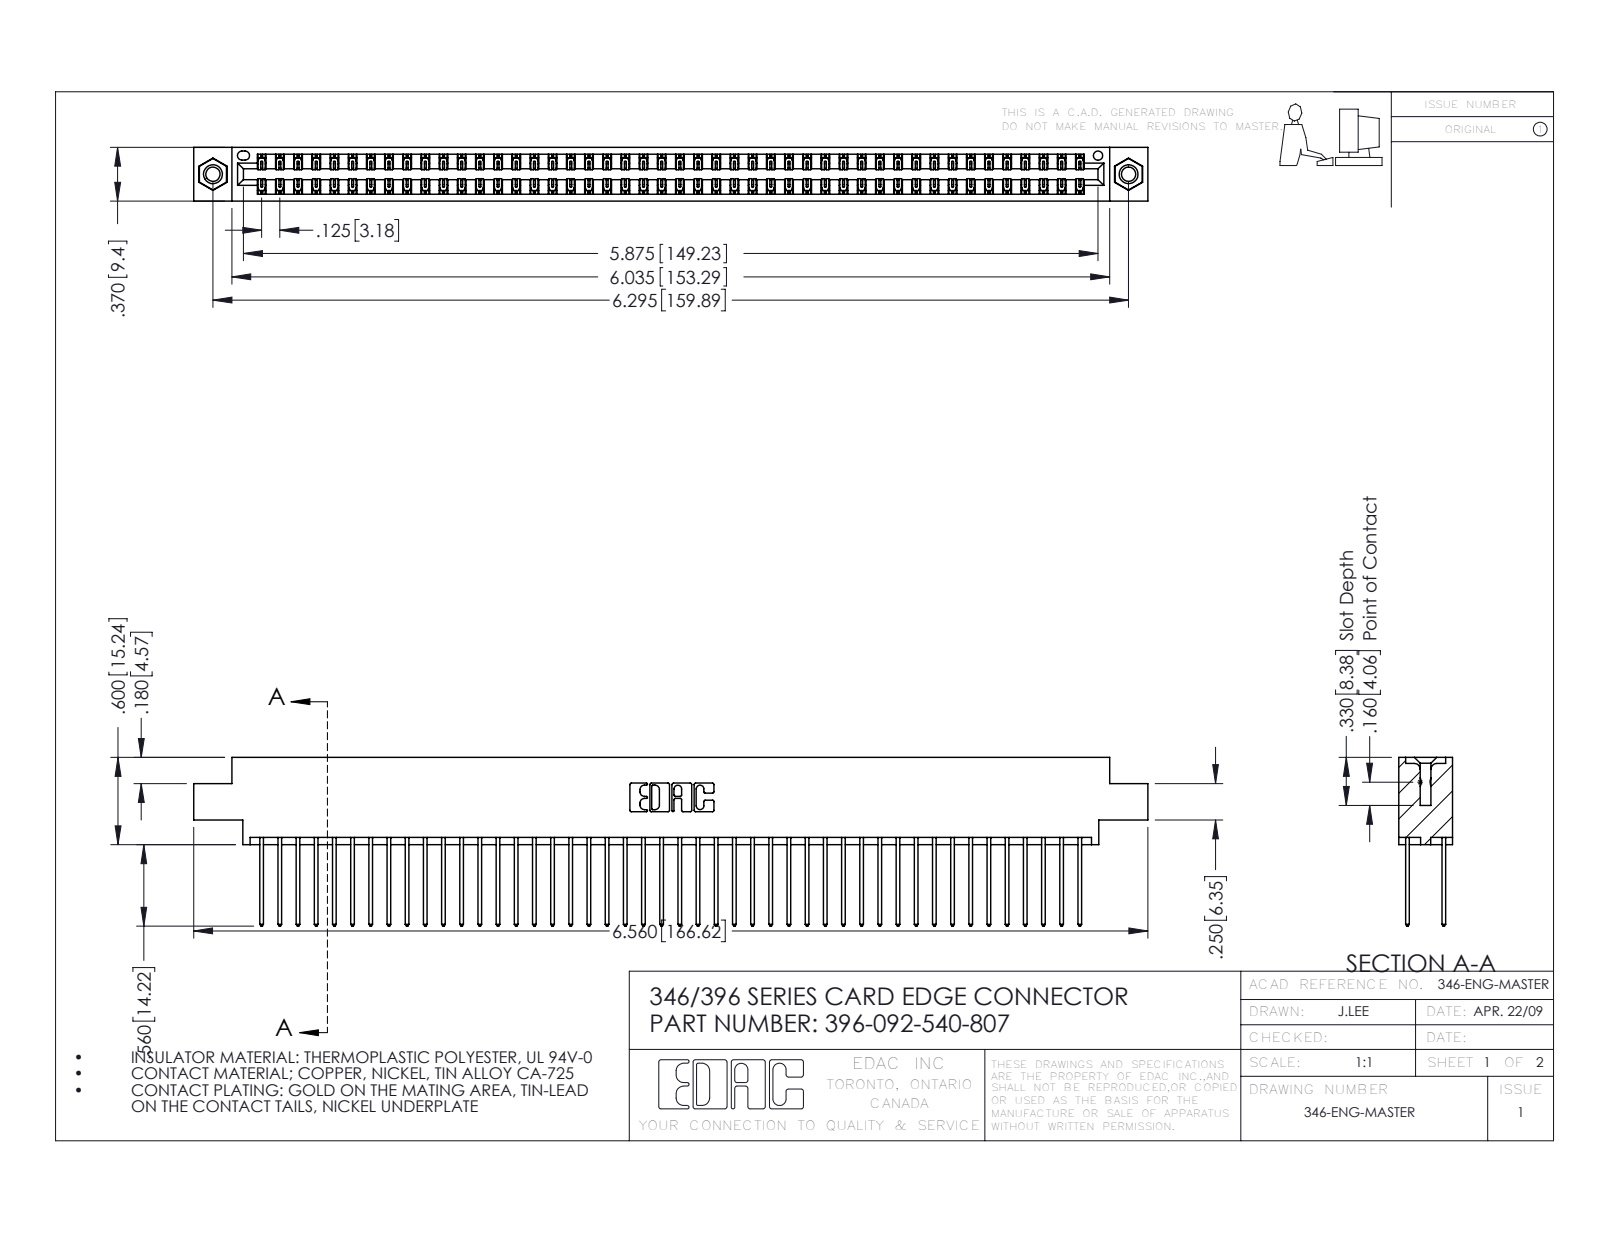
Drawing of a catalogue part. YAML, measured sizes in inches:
part_name: "396-092-540-807; 345-292-001_345-293-140; 345-250-001_345-250-005-103; 346 Part_0.170 Offset - 0.156 Dia-TI"
step_written_by: "SolidWorks 2016 (CONFIG_CONTROL_DESIGN)"
units: inches
bodies: {solids: 95, faces: 4970, planar: 3332, cylindrical: 1622, other: 16}
overall_size: [6.56, 1.16, 0.37]
volume: 1.004
surface_area: 38.05
round_holes:
  - {diameter: 0.098, count: 2}
  - {diameter: 0.125, count: 2}
  - {diameter: 0.156, count: 2}
  - {diameter: 0.064, count: 1}
round_bosses_or_shafts:
  - {diameter: 0.155, count: 2}
partial_cylinders:
  - {radius: 0.006, count: 138}
  - {radius: 0.01, count: 92}
  - {radius: 0.01, count: 22}
  - {radius: 0.007, count: 6}
  - {radius: 0.031, count: 6}
  - {radius: 0.026, count: 3}
  - {radius: 0.014, count: 2}
  - {radius: 0.022, count: 2}
face_to_face_distances: [0.048, 0.322, 0.25, 0.072, 0.298, 0.025, 0.37, 0.275, 0.222, 0.148]
hole_center_spacings: [0.246, 6.086, 6.295]
